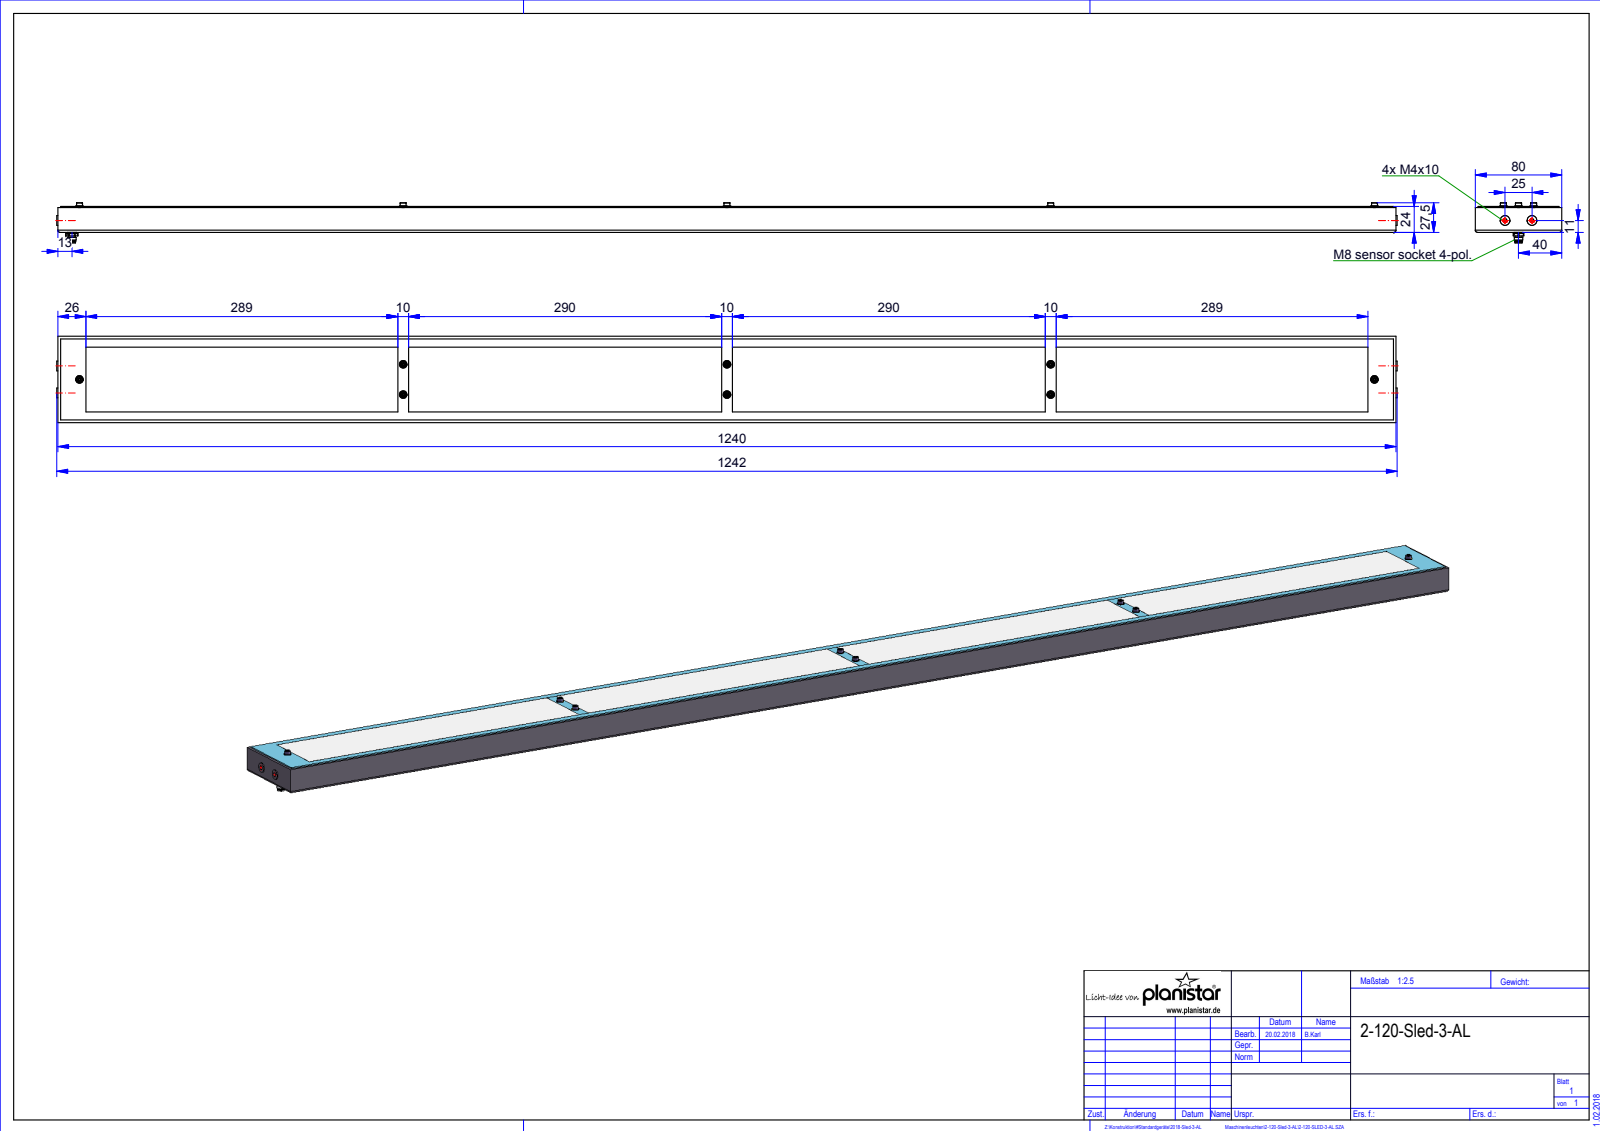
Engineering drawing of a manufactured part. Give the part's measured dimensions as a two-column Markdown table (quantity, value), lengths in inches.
| quantity | value |
| --- | --- |
| part name | Root; Baugruppe_Xled-2-VD; QUADER_0; 09-3391-00-04 (+2 more) |
| STEP written by | HiCAD 2015 2002.1 Build 408 (AUTOMOTIVE_DESIGN) |
| units | inches |
| bodies | 18 solids, 297 faces (99 planar, 169 cylindrical, 29 other) |
| overall size | 48.898 × 3.15 × 1.465 |
| volume | 144.6 in³ |
| surface area | 407.9 in² |
| round holes (diameter × count) | 0.126 × 8, 0.13 × 2, 0.157 × 2, 0.228 × 1 |
| round bosses / shafts (diameter × count) | 0.276 × 8, 0.217 × 8, 0.118 × 8, 0.097 × 8, 0.039 × 4, 0.354 × 2, 0.315 × 1, 0.283 × 1 |
| partial cylindrical surfaces (radius × count) | 0.009 × 48, 0.023 × 48, 0.079 × 4, 0.217 × 1 |
| main face-to-face distances | 0.943, 3.15, 0.945, 0.039, 0.906, 0.037, 0.098, 3.051, 48.819, 2.953 |
| hole center spacings | 11.811, 11.824, 11.862, 23.628, 35.437, 1.102, 12.099, 23.622 |
